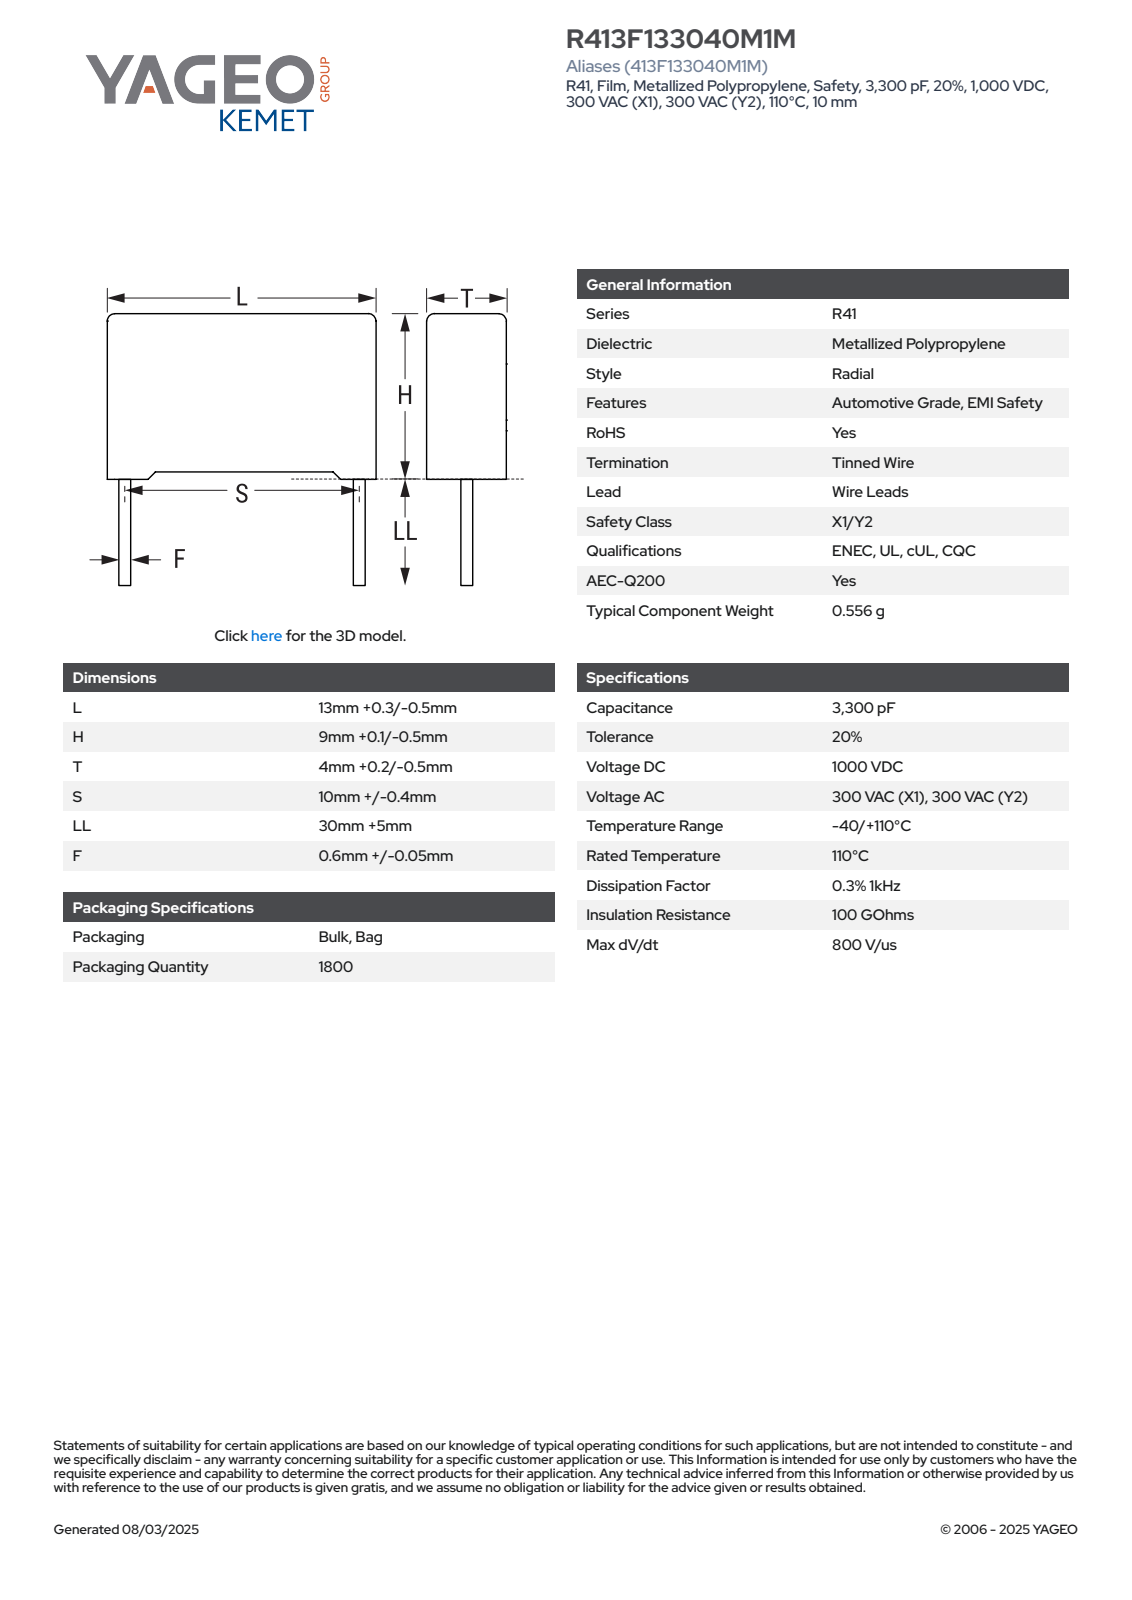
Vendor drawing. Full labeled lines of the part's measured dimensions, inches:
Part name (STEP PRODUCT): CFR_RB2_13X9X4_L13.3H9.1T4.2S10LL35F0.65
STEP written by: SolidWorks 2021 (AUTOMOTIVE_DESIGN)
Units: inches
Bodies: 4 solids, 85 faces (77 planar, 8 cylindrical, 0 other)
Overall size (bounding box): 1.736 × 0.524 × 0.166
Volume: 0.03 in³ · Surface area: 0.925 in²
Round bosses / shafts (diameter × count): ⌀0.026 ×2
Partial cylindrical surfaces — rounded edges, fillets, slot ends (radius × count): R0.02 ×4
Main face-to-face distances: 0.165, 0.329, 0.524, 0.017, 0.148, 0.03, 0.358, 0.131, 0.012, 0.346
